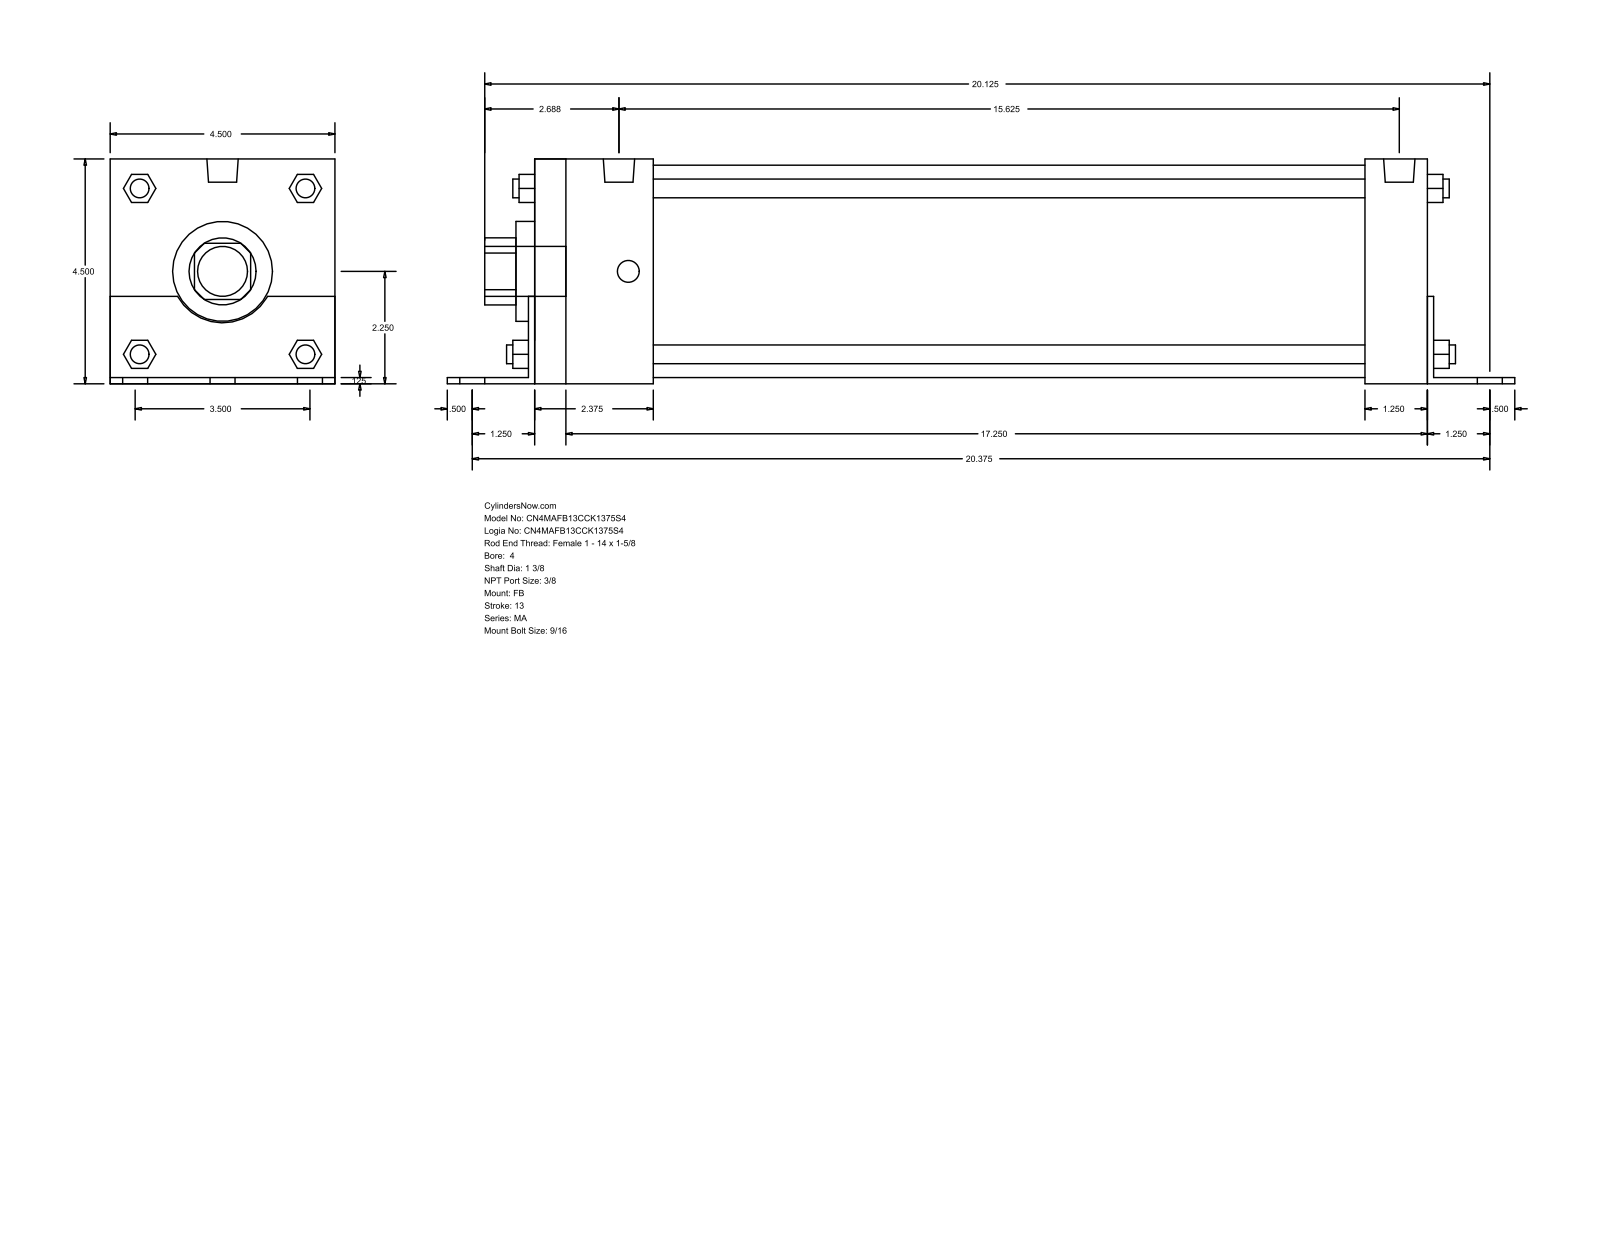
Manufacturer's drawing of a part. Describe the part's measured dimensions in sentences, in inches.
The part is named "MA_FB__0400_1.375". Its 3-D file was written by "GSSL Pune (CONFIG_CONTROL_DESIGN)". It is 0 solids with 140 faces: 105 planar, 35 cylindrical and 0 other. Overall it measures 21.375 by 4.502 by 4.5 inches. Round holes: 1 of diameter 1.375, 1 of diameter 2, 1 of diameter 4.25. Round bosses or shafts: 6 of diameter 0.563, 4 of diameter 0.437, 4 of diameter 0.375, 2 of diameter 0.627, 1 of diameter 1. Partial cylindrical surfaces (rounded edges, fillets, slot ends): 1 of radius 0.672, 1 of radius 1.03. The main face-to-face distances are 4.5, 0.125, 4.502, 0.123, 4.377, 18, 17.875, 2.375, 18.125, 1.25.
